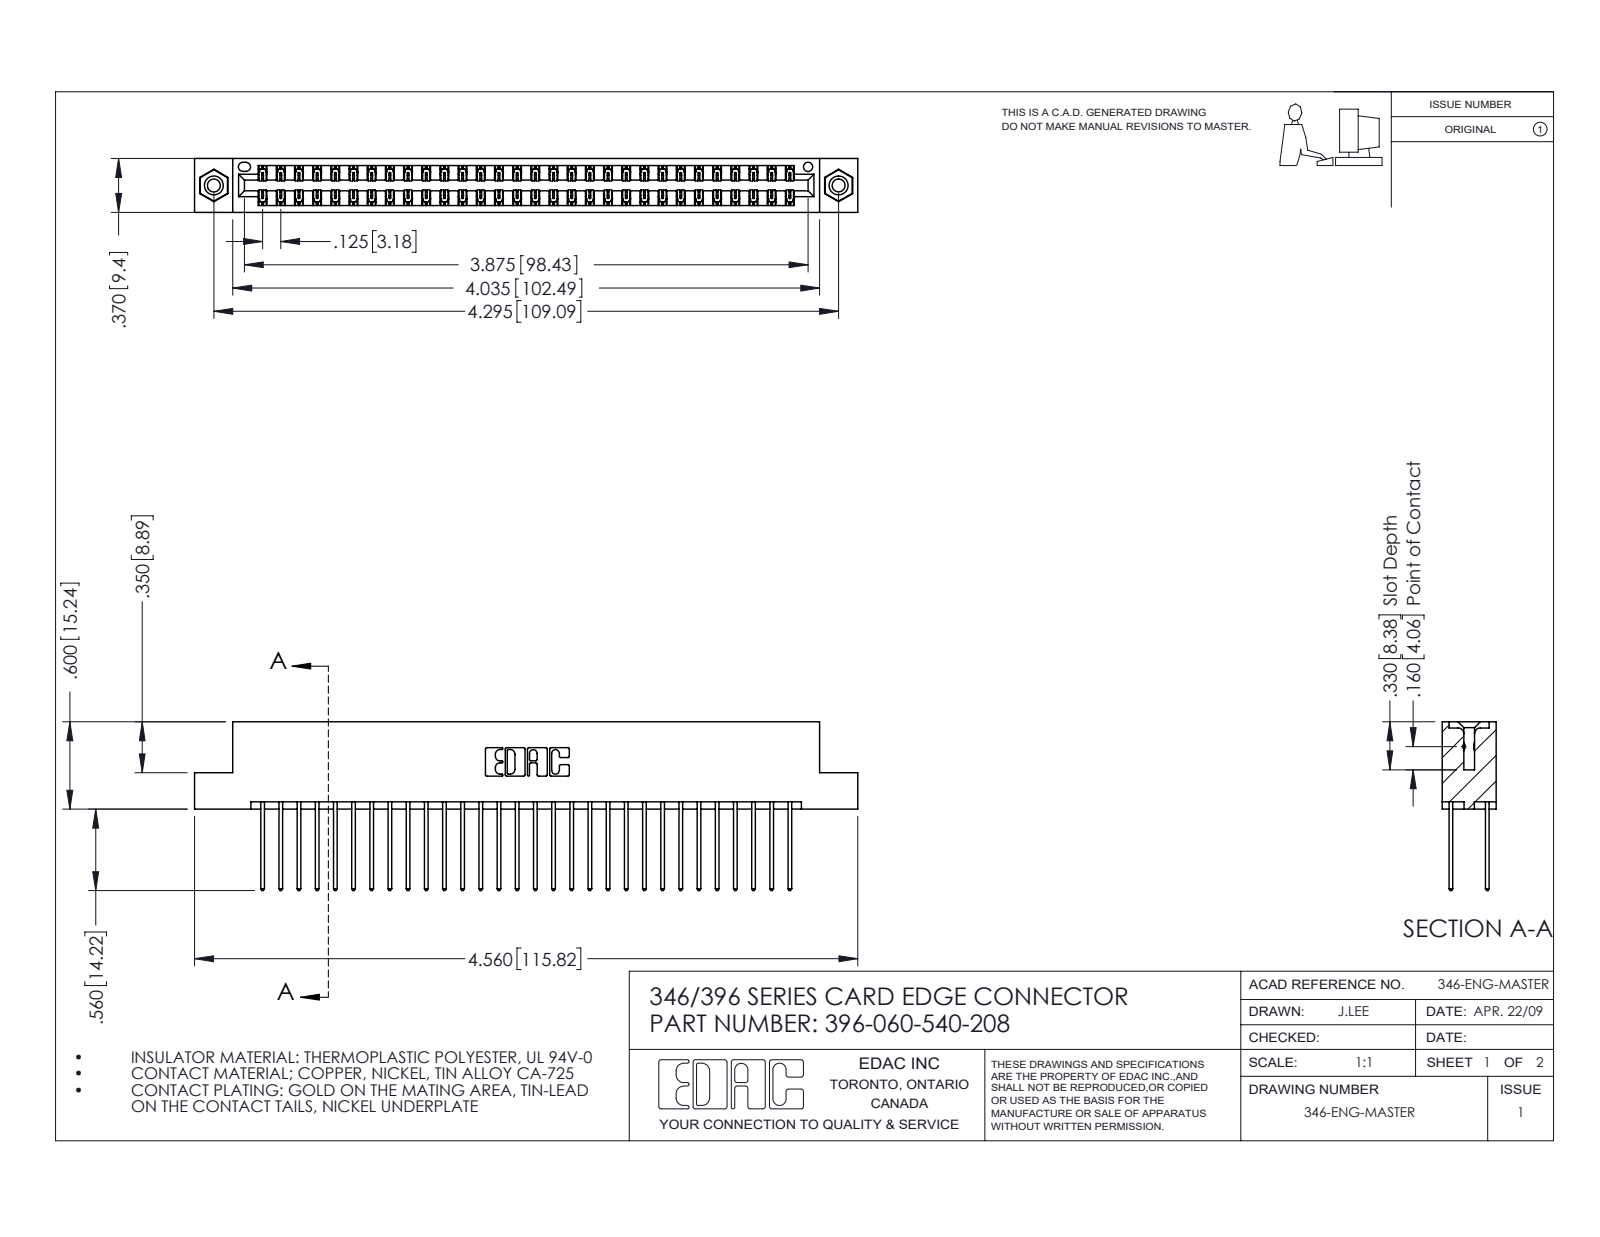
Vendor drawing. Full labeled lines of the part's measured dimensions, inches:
Part name (STEP PRODUCT): 346 Part_Flush Mounting Lugs - 0.156 Dia-TI; 345-292-001_345-293-140; 345-250-001_345-250-003-102; 396-060-540-208
STEP written by: SolidWorks 2016 (CONFIG_CONTROL_DESIGN)
Units: inches
Bodies: 63 solids, 3302 faces (2208 planar, 1078 cylindrical, 16 other)
Overall size (bounding box): 4.56 × 1.16 × 0.37
Volume: 0.697 in³ · Surface area: 25.74 in²
Round holes (diameter × count): ⌀0.089 ×2, ⌀0.125 ×2, ⌀0.156 ×2, ⌀0.064 ×1
Round bosses / shafts (diameter × count): ⌀0.155 ×2
Partial cylindrical surfaces — rounded edges, fillets, slot ends (radius × count): R0.006 ×90, R0.01 ×60, R0.01 ×22, R0.007 ×6, R0.031 ×6, R0.026 ×3, R0.014 ×2, R0.022 ×2
Main face-to-face distances: 0.048, 0.322, 0.25, 0.072, 0.298, 0.025, 0.37, 0.275, 0.148, 0.222
Hole centre spacings: 0.246, 4.087, 4.295
